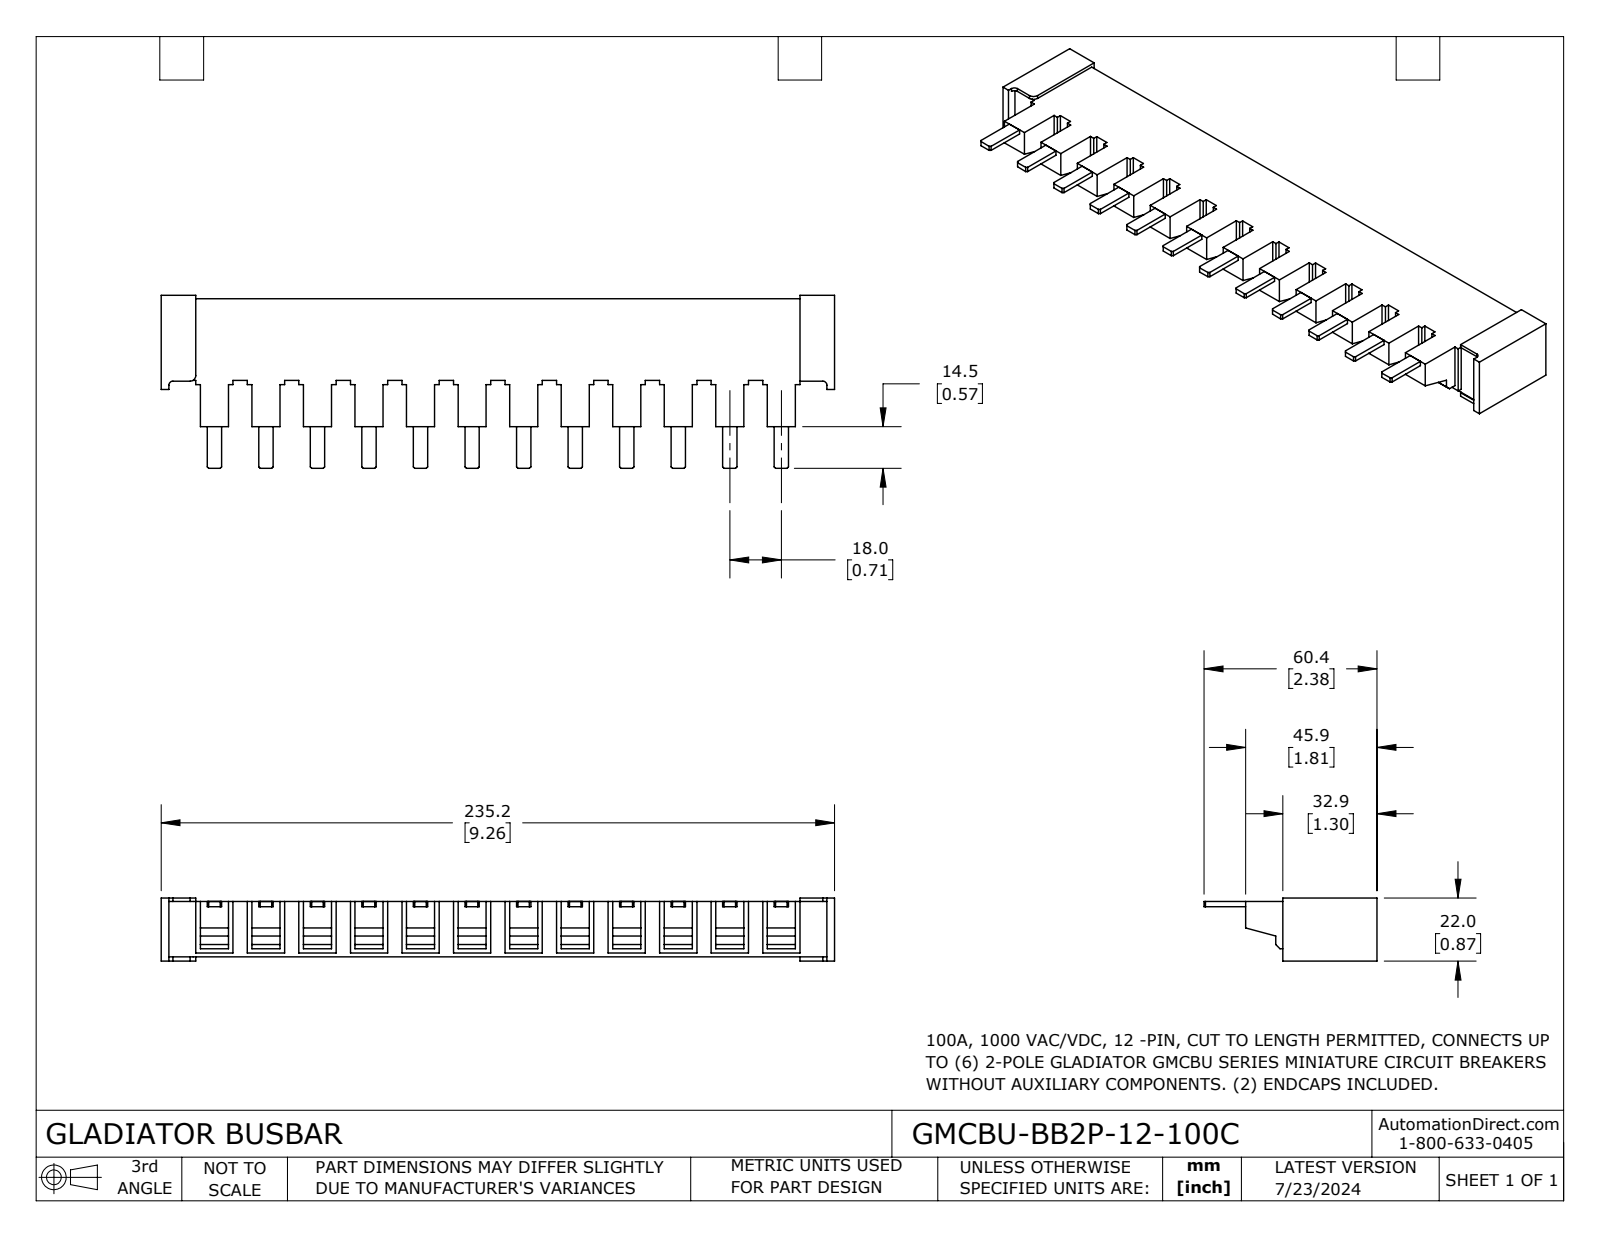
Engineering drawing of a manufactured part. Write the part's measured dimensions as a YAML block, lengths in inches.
part_name: "GMCBU-BB2P-12-100C"
step_written_by: "SolidWorks 2023 (CONFIG_CONTROL_DESIGN)"
units: inches
bodies: {solids: 1, faces: 248, planar: 242, cylindrical: 6, other: 0}
overall_size: [9.26, 2.378, 0.866]
volume: 9.716
surface_area: 54.83
partial_cylinders:
  - {radius: 0.055, count: 2}
  - {radius: 0.079, count: 1}
face_to_face_distances: [0.76, 0.709, 1.417, 2.126, 0.059, 2.835, 1.122, 3.543, 0.047, 4.252]
